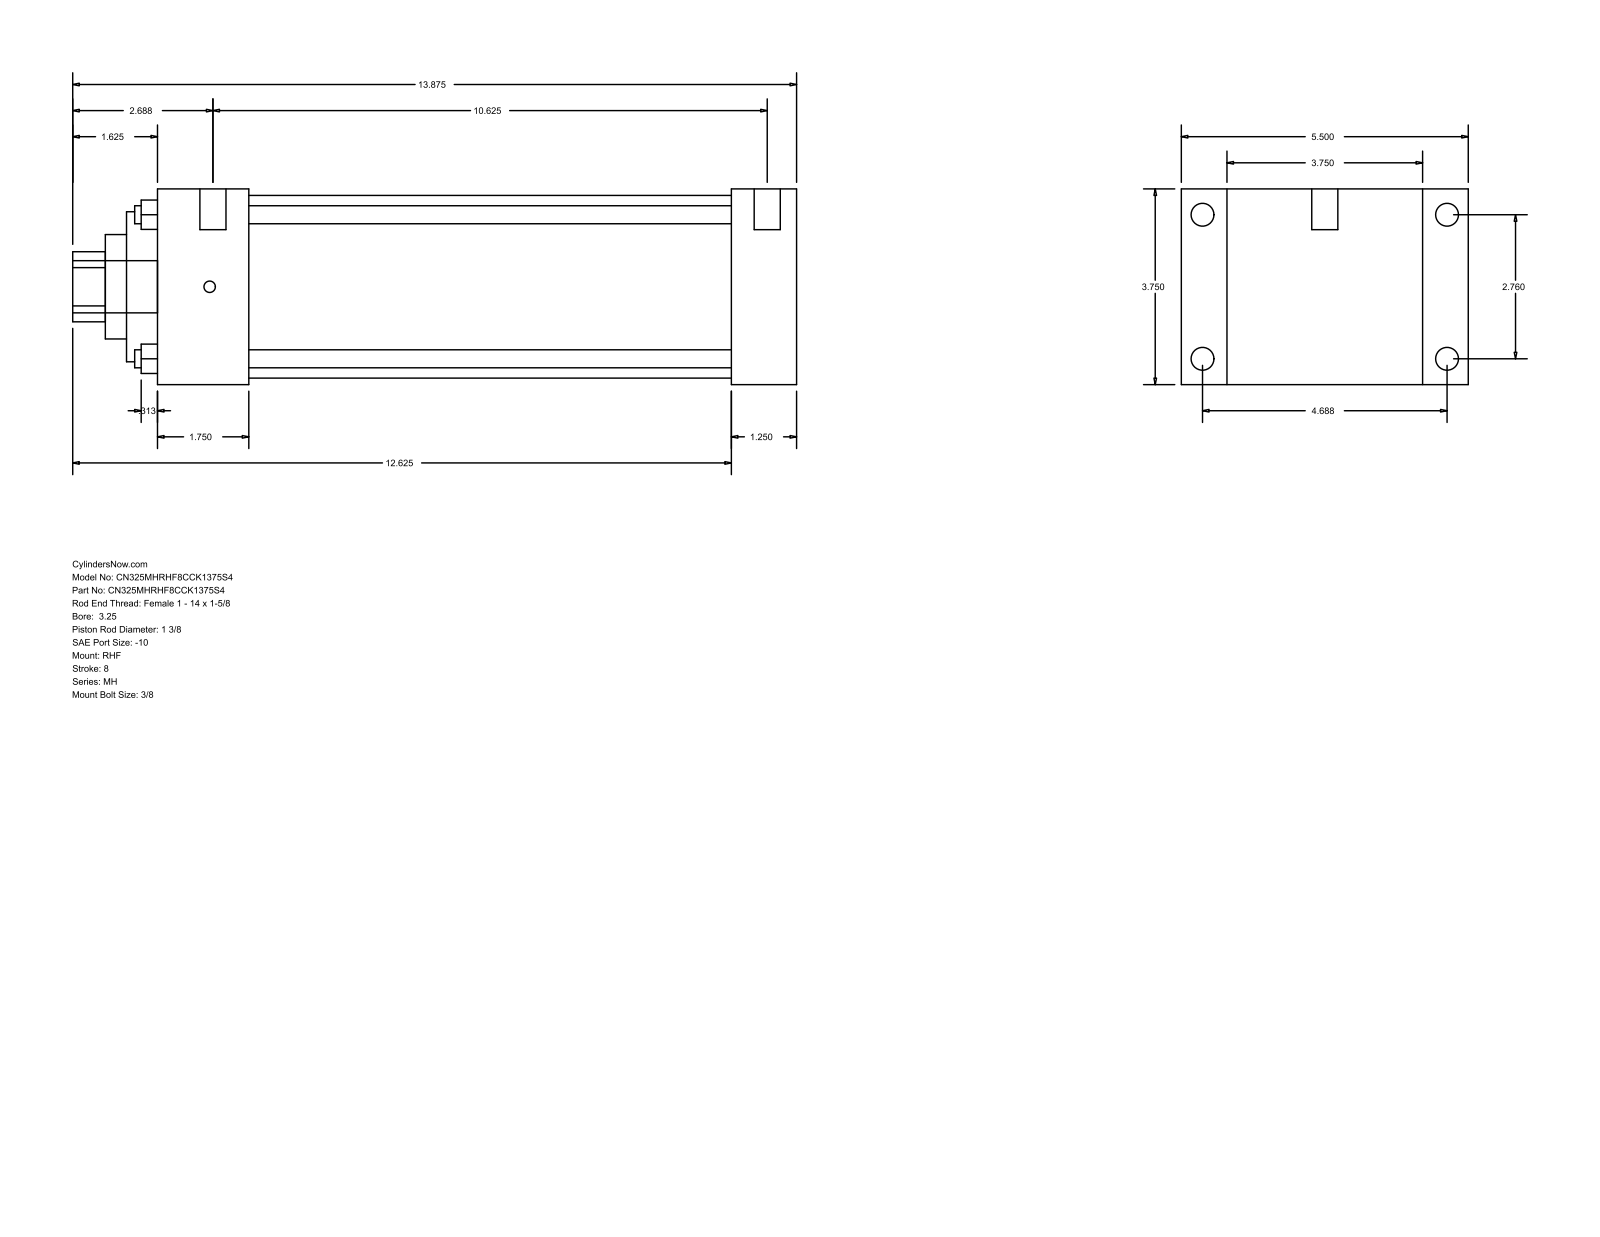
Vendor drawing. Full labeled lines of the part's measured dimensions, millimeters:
Part name (STEP PRODUCT): MH_RHF__0325_1.375
STEP written by: GSSL Pune (CONFIG_CONTROL_DESIGN)
Units: millimetres
Bodies: 0 solids, 90 faces (61 planar, 29 cylindrical, 0 other)
Overall size (bounding box): 352.43 × 139.7 × 95.25
Round holes (diameter × count): ⌀8.76 ×4, ⌀34.92 ×1, ⌀50.8 ×1, ⌀73.03 ×1, ⌀88.9 ×1
Round bosses / shafts (diameter × count): ⌀11.13 ×4, ⌀5.56 ×4, ⌀12.7 ×2, ⌀25.4 ×1
Partial cylindrical surfaces — rounded edges, fillets, slot ends (radius × count): R17.06 ×1
Main face-to-face distances: 95.24, 31.75, 22.23, 117.47, 279.41, 311.16, 139.7, 44.45, 234.96, 266.71
Hole centre spacings: 49.57, 70.1, 99.14
